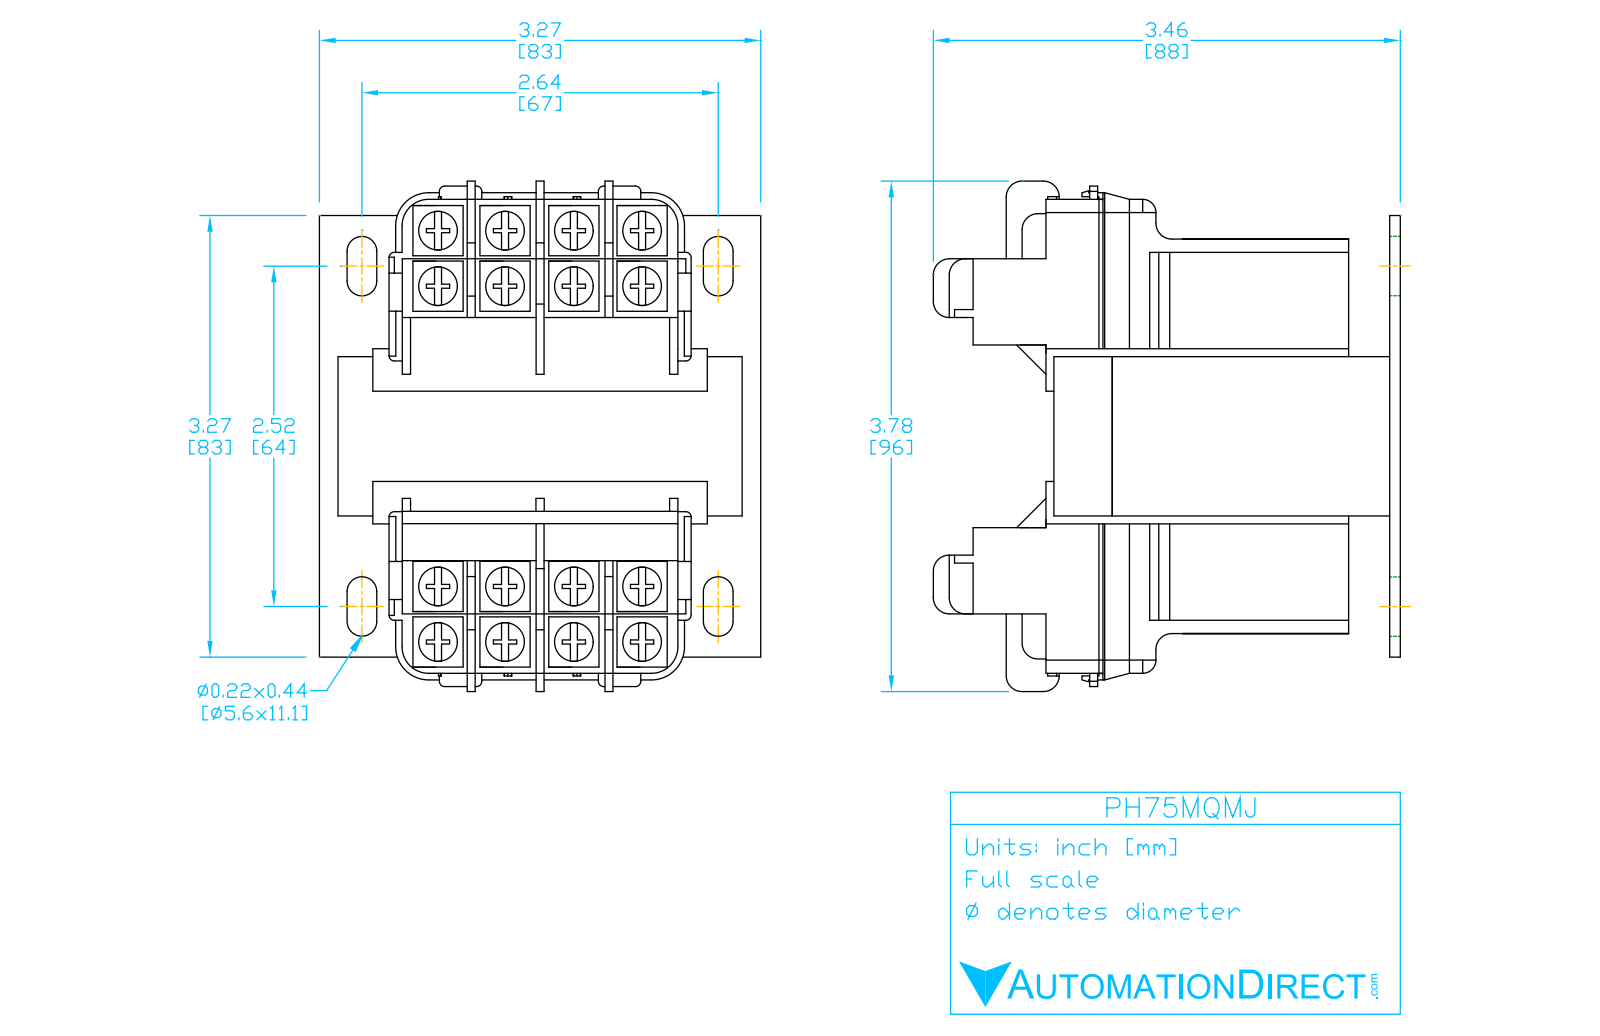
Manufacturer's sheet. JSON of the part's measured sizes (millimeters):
{"part_name": "PH75MQMJ", "step_written_by": "SolidWorks 2017 (AUTOMOTIVE_DESIGN)", "units": "millimeters", "bodies": {"solids": 8, "faces": 386, "planar": 276, "cylindrical": 102, "other": 8}, "overall_size": [96, 88.2, 82.6], "volume_mm3": 381500, "surface_area_mm2": 72260, "round_holes": [[4, 4]], "partial_cylinders_radius": [[1, 32], [2, 20], [2.8, 8], [5, 8], [3, 4], [6.2, 4], [2, 2]], "face_to_face_distances": [30, 54.3, 9.2, 50.8, 3.5, 10.1, 66.1, 32, 60, 63.5], "hole_center_spacings": [22.2, 66.6, 70.3]}
